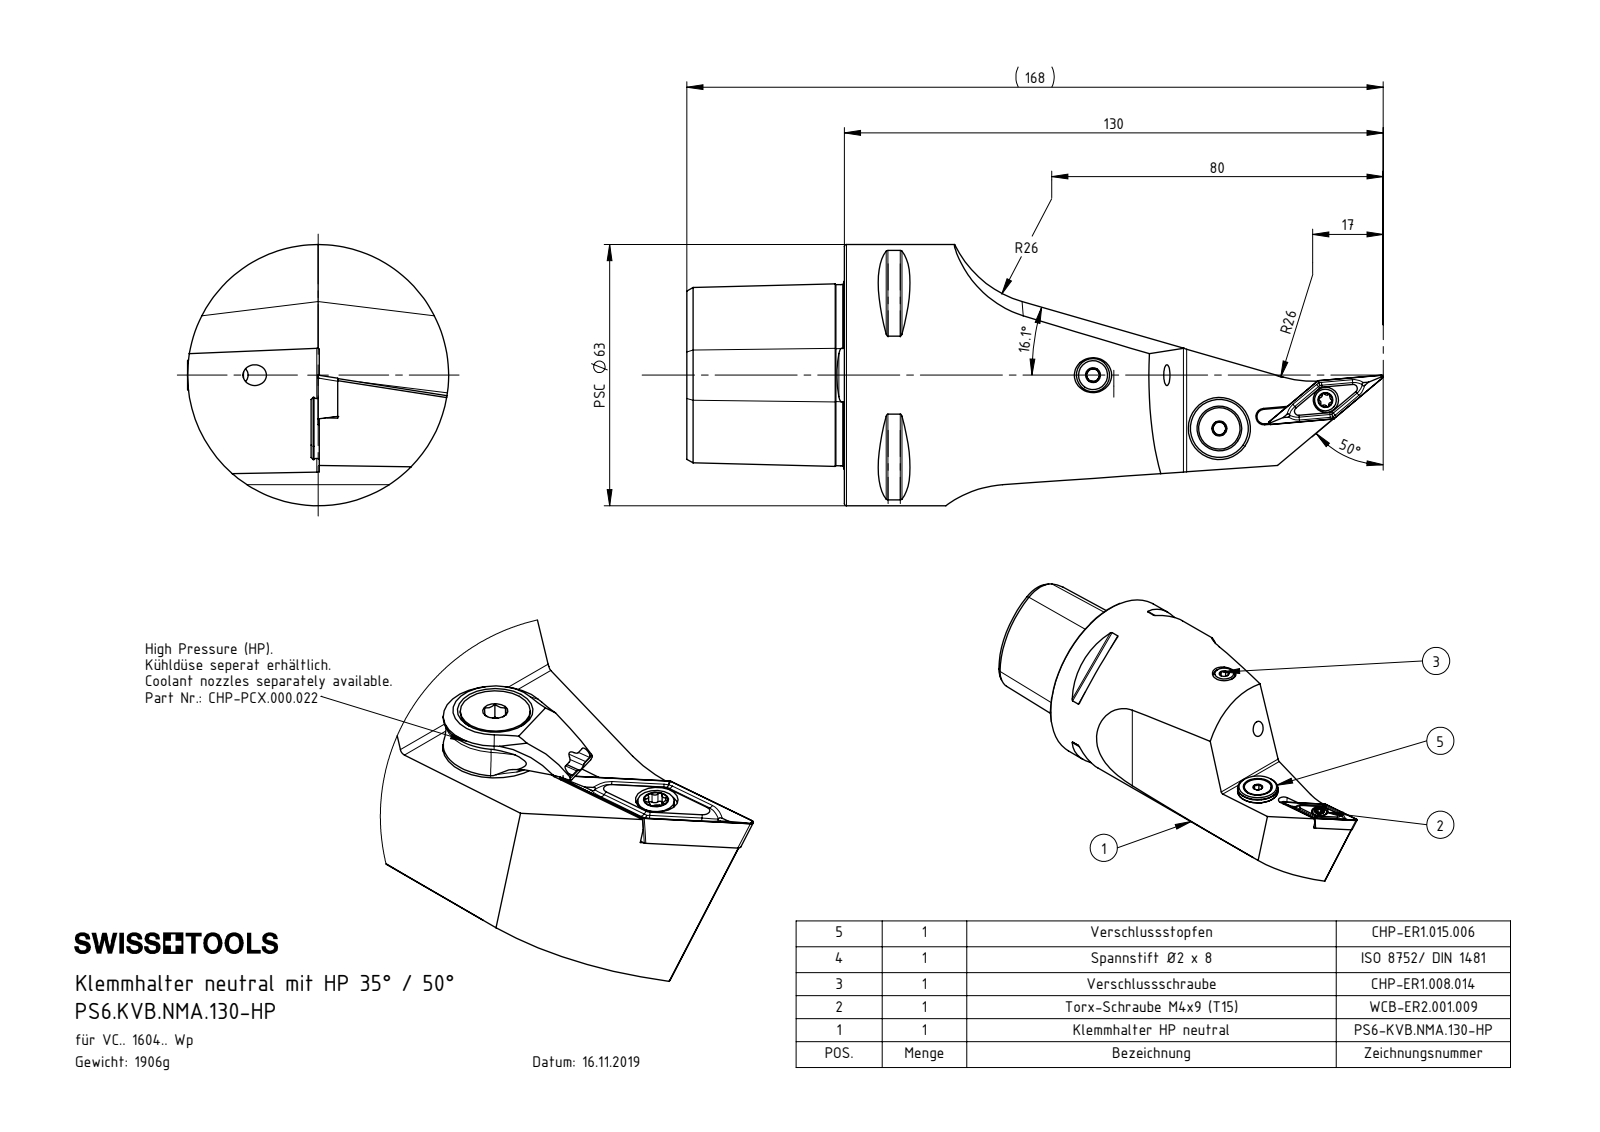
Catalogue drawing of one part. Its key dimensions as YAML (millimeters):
part_name: "WCB-ER2.001.009_A; DIN 3771 - 13x1; CHP-ER1.008.014_A; PS6.KVB.NMA.130-HP (+7 more)"
step_written_by: "SolidWorks 2017 (AUTOMOTIVE_DESIGN)"
units: millimeters
bodies: {solids: 9, faces: 373, planar: 104, cylindrical: 94, other: 175}
overall_size: [168, 63, 63]
volume: 243870
surface_area: 39825
round_holes:
  - {diameter: 4.2, count: 2}
  - {diameter: 5, count: 2}
  - {diameter: 1.2, count: 1}
  - {diameter: 2, count: 1}
  - {diameter: 3, count: 1}
  - {diameter: 3.3, count: 1}
  - {diameter: 4, count: 1}
  - {diameter: 4.4, count: 1}
  - {diameter: 5.3, count: 1}
  - {diameter: 6.1, count: 1}
  - {diameter: 7, count: 1}
  - {diameter: 8.1, count: 1}
round_bosses_or_shafts:
  - {diameter: 63, count: 1}
  - {diameter: 14.85, count: 1}
  - {diameter: 13.4, count: 1}
  - {diameter: 10, count: 1}
  - {diameter: 8, count: 1}
  - {diameter: 5.5, count: 1}
  - {diameter: 5.25, count: 1}
  - {diameter: 5, count: 1}
partial_cylinders:
  - {radius: 0.5, count: 10}
  - {radius: 1, count: 7}
  - {radius: 0.34, count: 6}
  - {radius: 0.59, count: 6}
  - {radius: 6, count: 4}
  - {radius: 26, count: 4}
  - {radius: 0.8, count: 2}
  - {radius: 1.1, count: 2}
face_to_face_distances: [38, 24.88, 115, 77, 11, 27, 88, 4.46, 55.8, 4.5]
hole_center_spacings: [4.5, 23.24, 23.35, 26.5, 26.62, 27.5, 79.54, 81.59]
